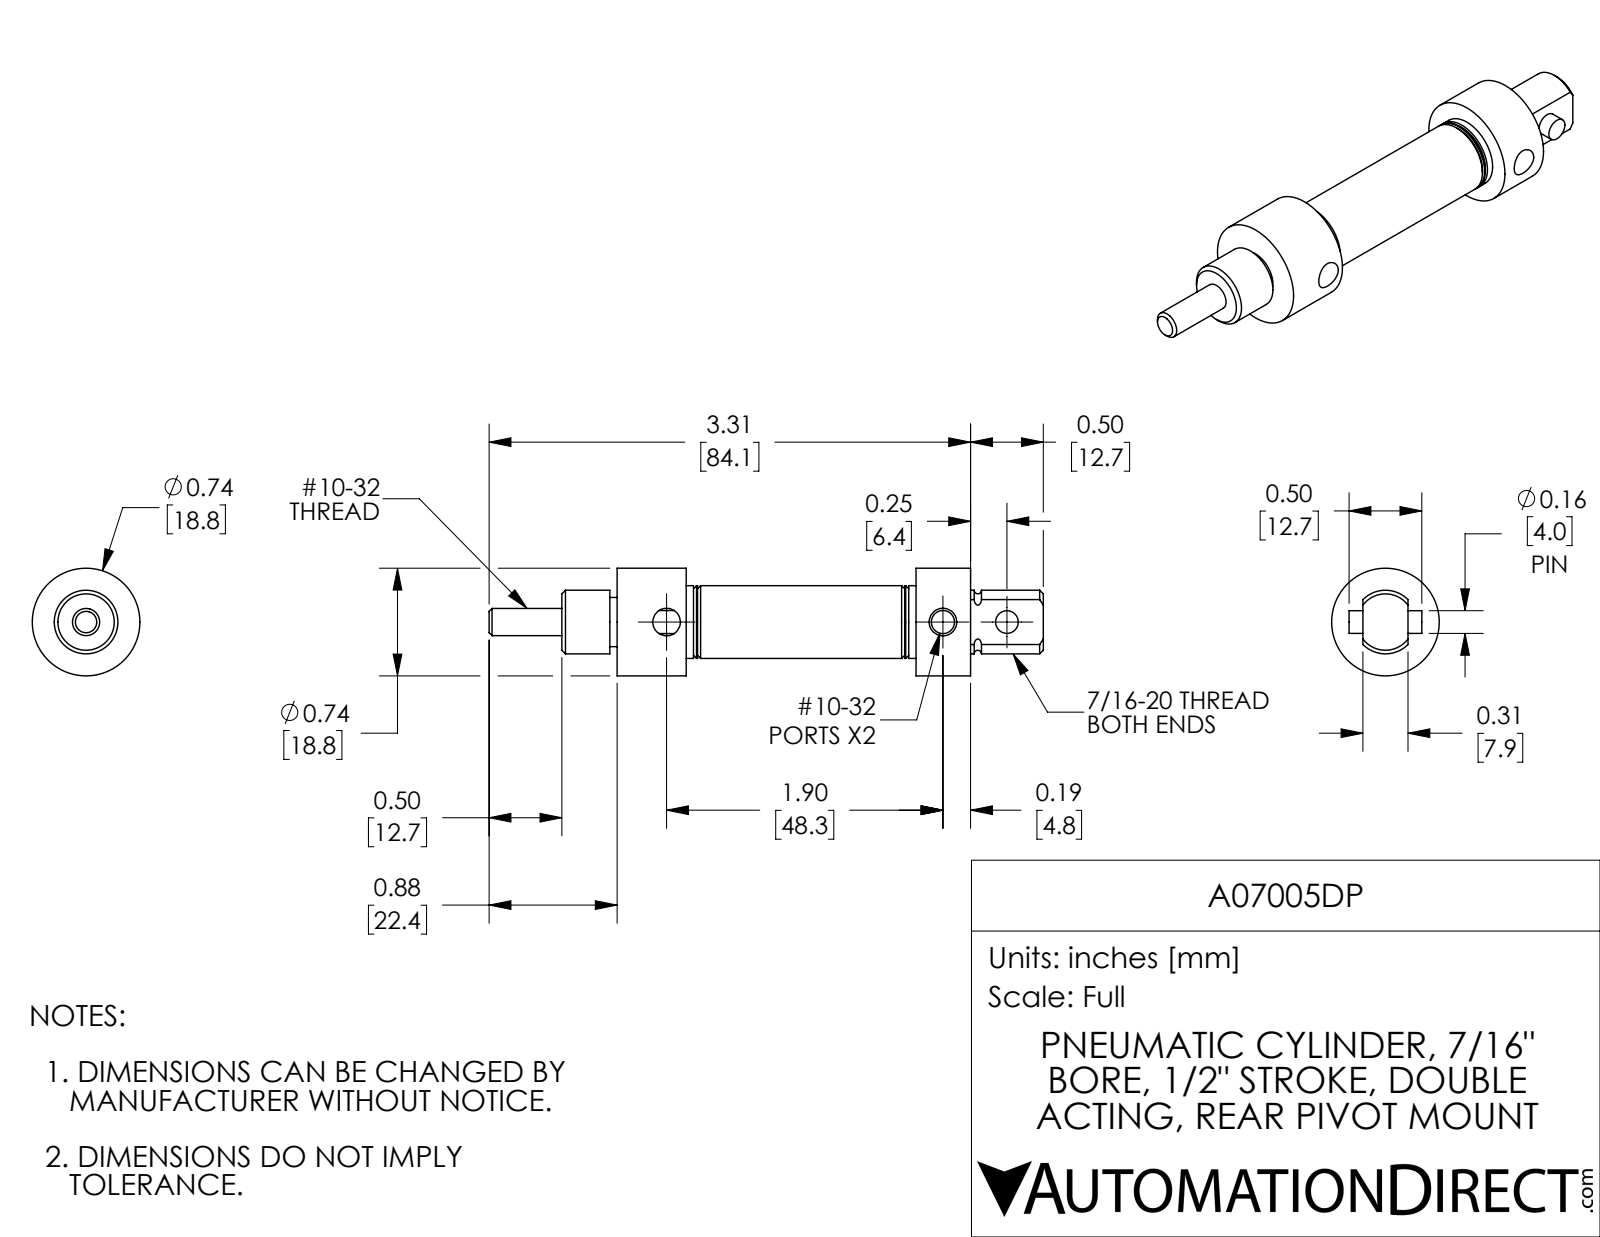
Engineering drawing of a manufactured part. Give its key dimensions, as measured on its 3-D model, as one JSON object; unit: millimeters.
{"part_name": "A07005DP; A07005DP-Rod; A07005DP-Pin; A07005DP-MainBody", "step_written_by": "SolidWorks 2017 (AUTOMOTIVE_DESIGN)", "units": "millimeters", "bodies": {"solids": 3, "faces": 89, "planar": 23, "cylindrical": 44, "other": 22}, "overall_size": [96.8, 18.8, 18.8], "volume_mm3": 11800, "surface_area_mm2": 8065, "round_holes": [[4, 2], [4.8, 2], [4, 1], [4.7, 1]], "round_bosses_or_shafts": [[18.8, 1], [12.7, 1], [11.1, 1], [8.6, 1]], "face_to_face_distances": [43.6, 18.2, 12.7, 30.9, 61.7, 52.2, 49.7, 31.5, 12.1, 9.5], "hole_center_spacings": [11.2, 48.3, 59.4]}
